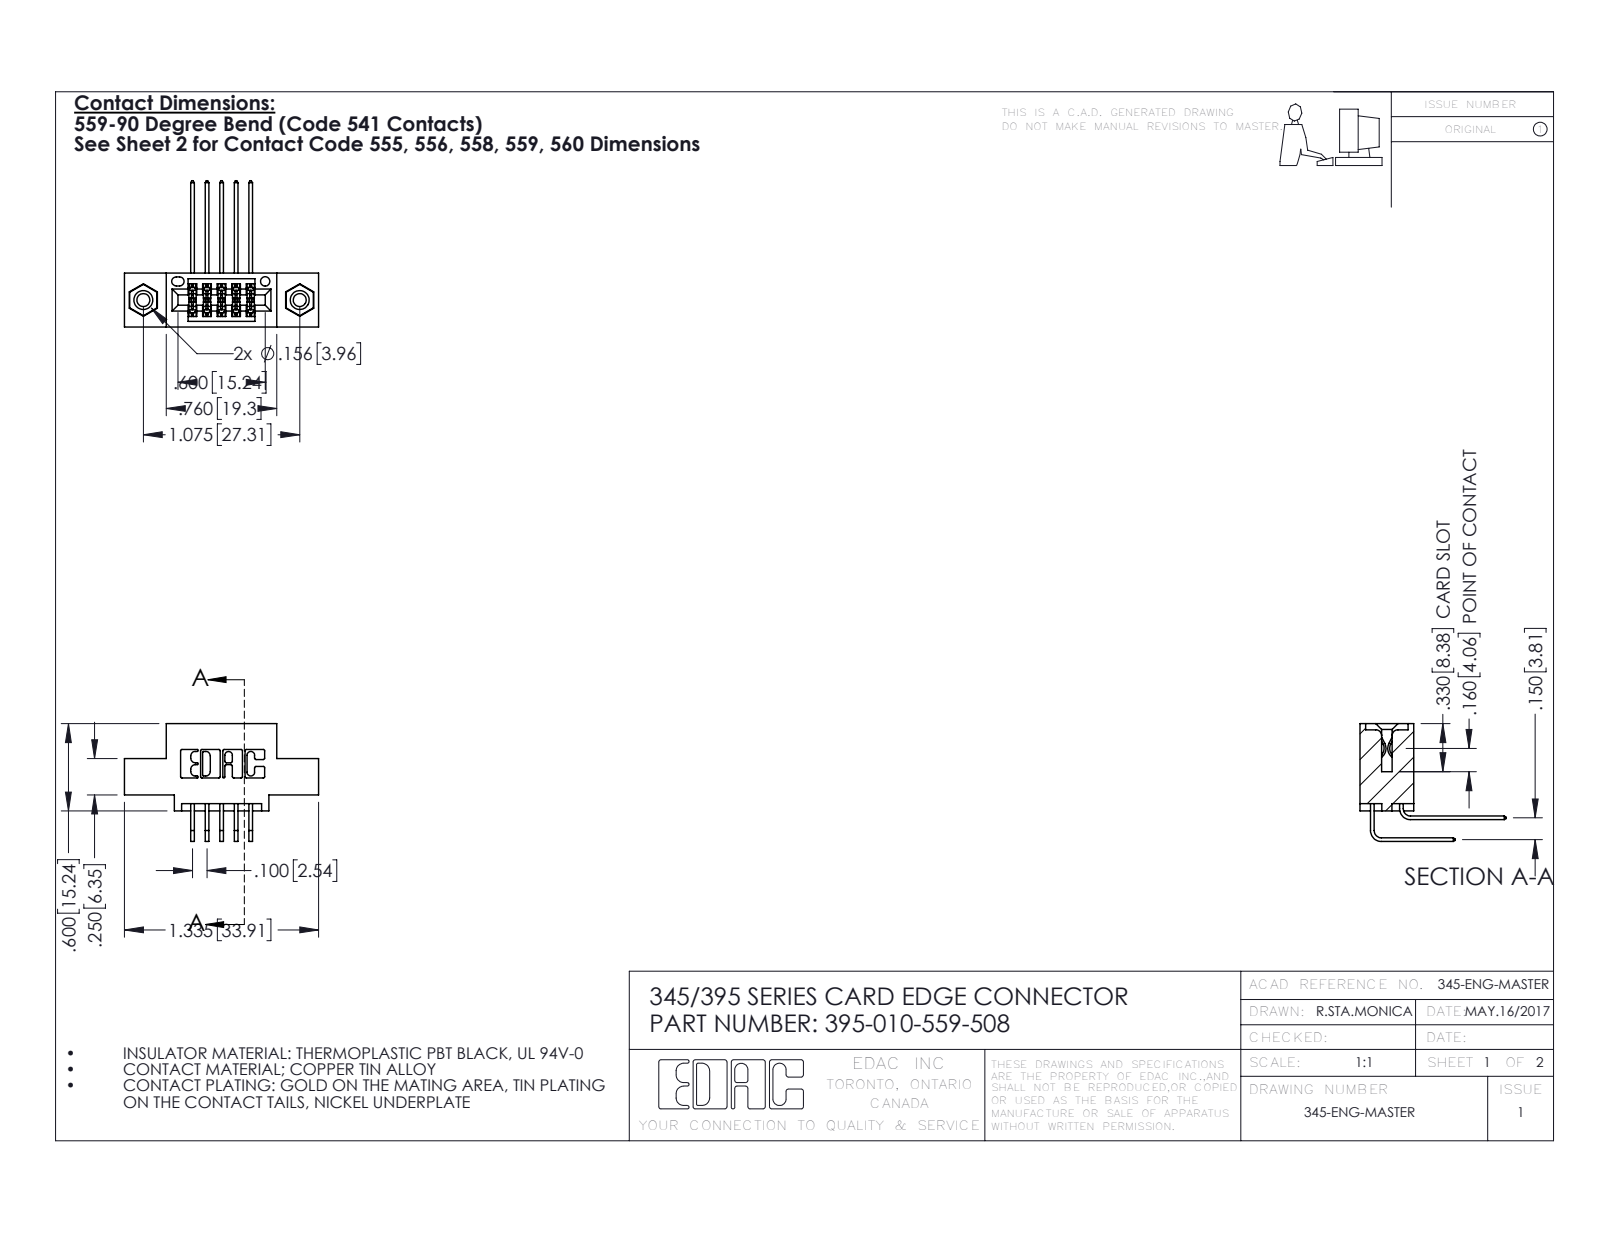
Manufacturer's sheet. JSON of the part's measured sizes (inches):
{"part_name": "395-010-559-508; 345-250-001_345-250-003-102; 345-292-001_558 559 Tail - 1; 345-292-001_559 Tail - 2 (+1 more)", "step_written_by": "SolidWorks 2016 (CONFIG_CONTROL_DESIGN)", "units": "inches", "bodies": {"solids": 13, "faces": 710, "planar": 466, "cylindrical": 228, "other": 16}, "overall_size": [1.335, 1.005, 0.809], "volume_in3": 0.179, "surface_area_in2": 6.184, "round_holes": [[0.089, 2], [0.125, 2], [0.156, 2], [0.064, 1]], "round_bosses_or_shafts": [[0.155, 2]], "partial_cylinders_radius": [[0.01, 22], [0.006, 16], [0.007, 6], [0.031, 6], [0.026, 3], [0.014, 2], [0.019, 2], [0.022, 2]], "face_to_face_distances": [0.2, 0.37, 0.1, 0.072, 0.298, 0.15, 0.098, 0.272, 0.025, 0.25], "hole_center_spacings": [0.27, 0.847, 1.075]}
